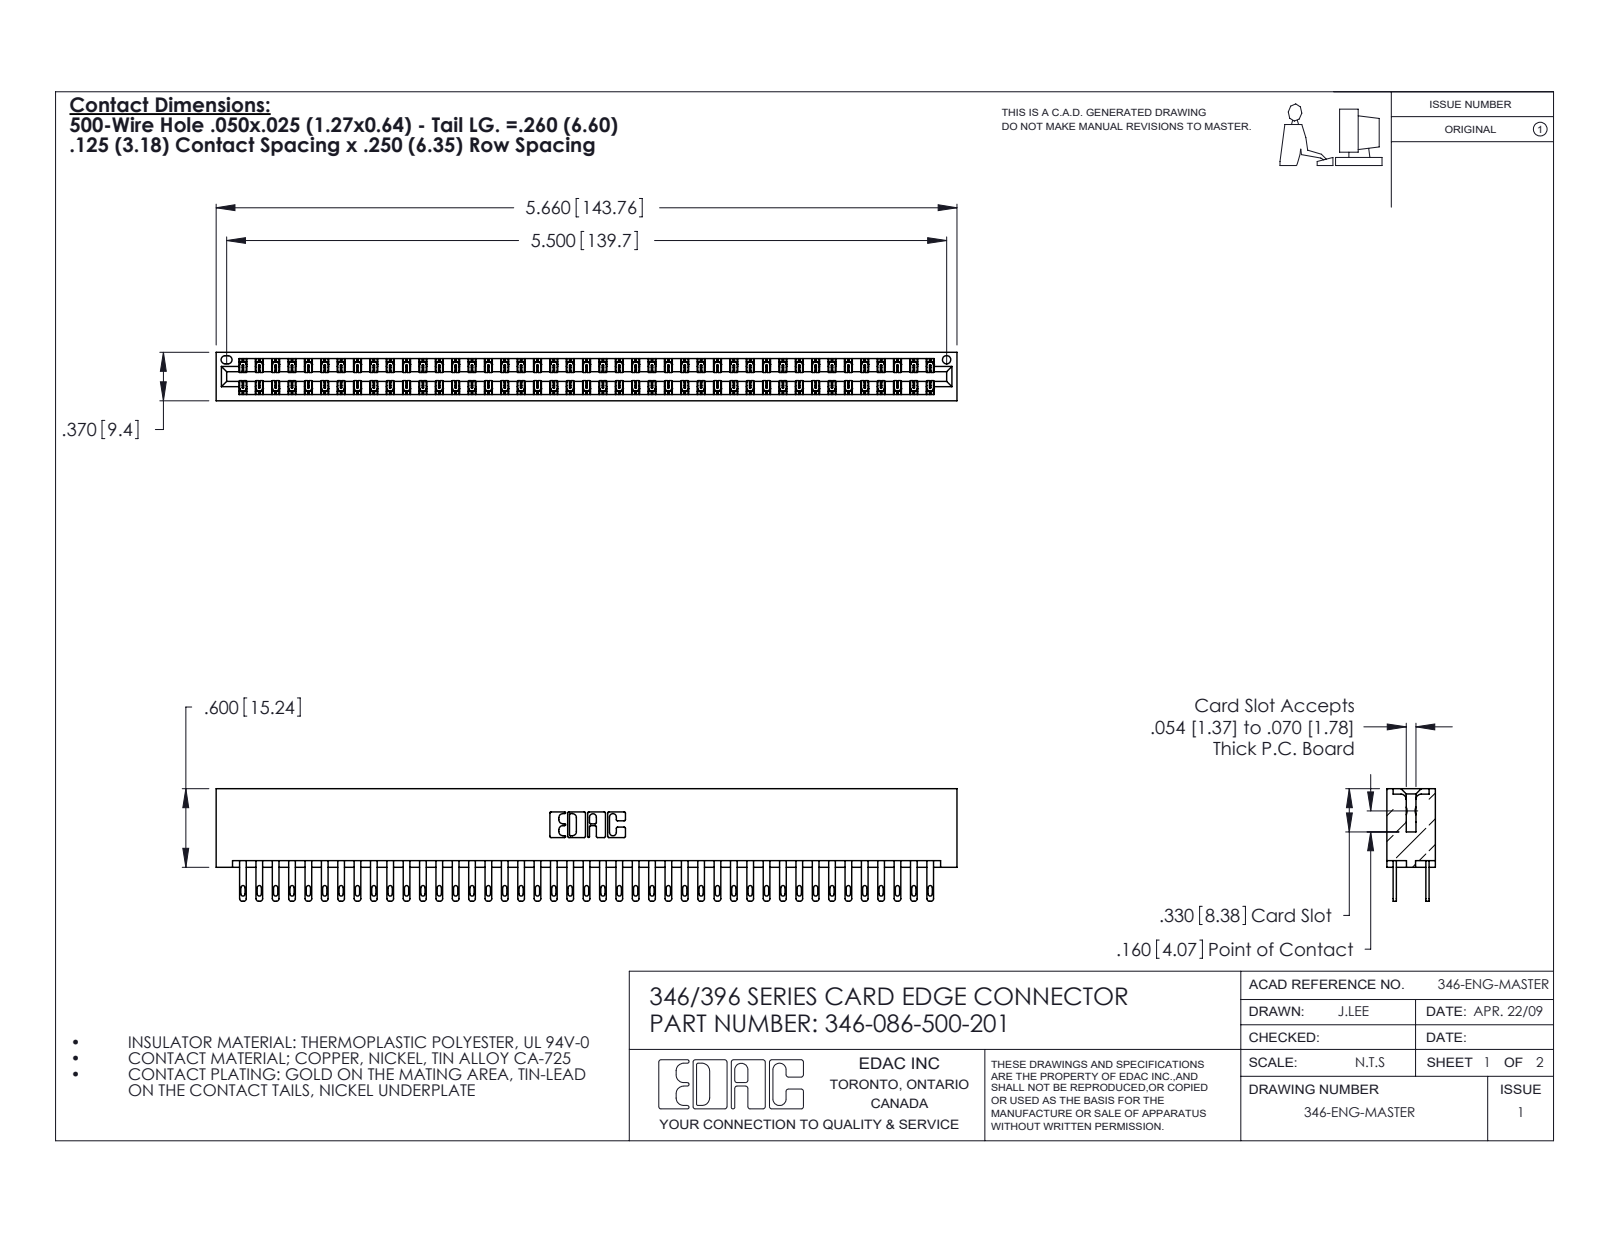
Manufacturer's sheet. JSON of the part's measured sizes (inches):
{"part_name": "346 Part_No Mounting Lugs; 345-292-001_345-293-100; 346-086-500-201", "step_written_by": "SolidWorks 2020 (CONFIG_CONTROL_DESIGN)", "units": "inches", "bodies": {"solids": 87, "faces": 4242, "planar": 2566, "cylindrical": 1676, "other": 0}, "overall_size": [5.66, 0.86, 0.37], "volume_in3": 0.907, "surface_area_in2": 33.34, "round_holes": [[0.064, 1]], "partial_cylinders_radius": [[0.006, 129], [0.016, 86], [0.02, 86], [0.01, 22], [0.007, 6], [0.031, 6], [0.026, 3], [0.014, 2]], "face_to_face_distances": [0.048, 0.322, 0.25, 0.072, 0.298, 0.025, 0.37, 0.275, 0.148, 0.222]}
